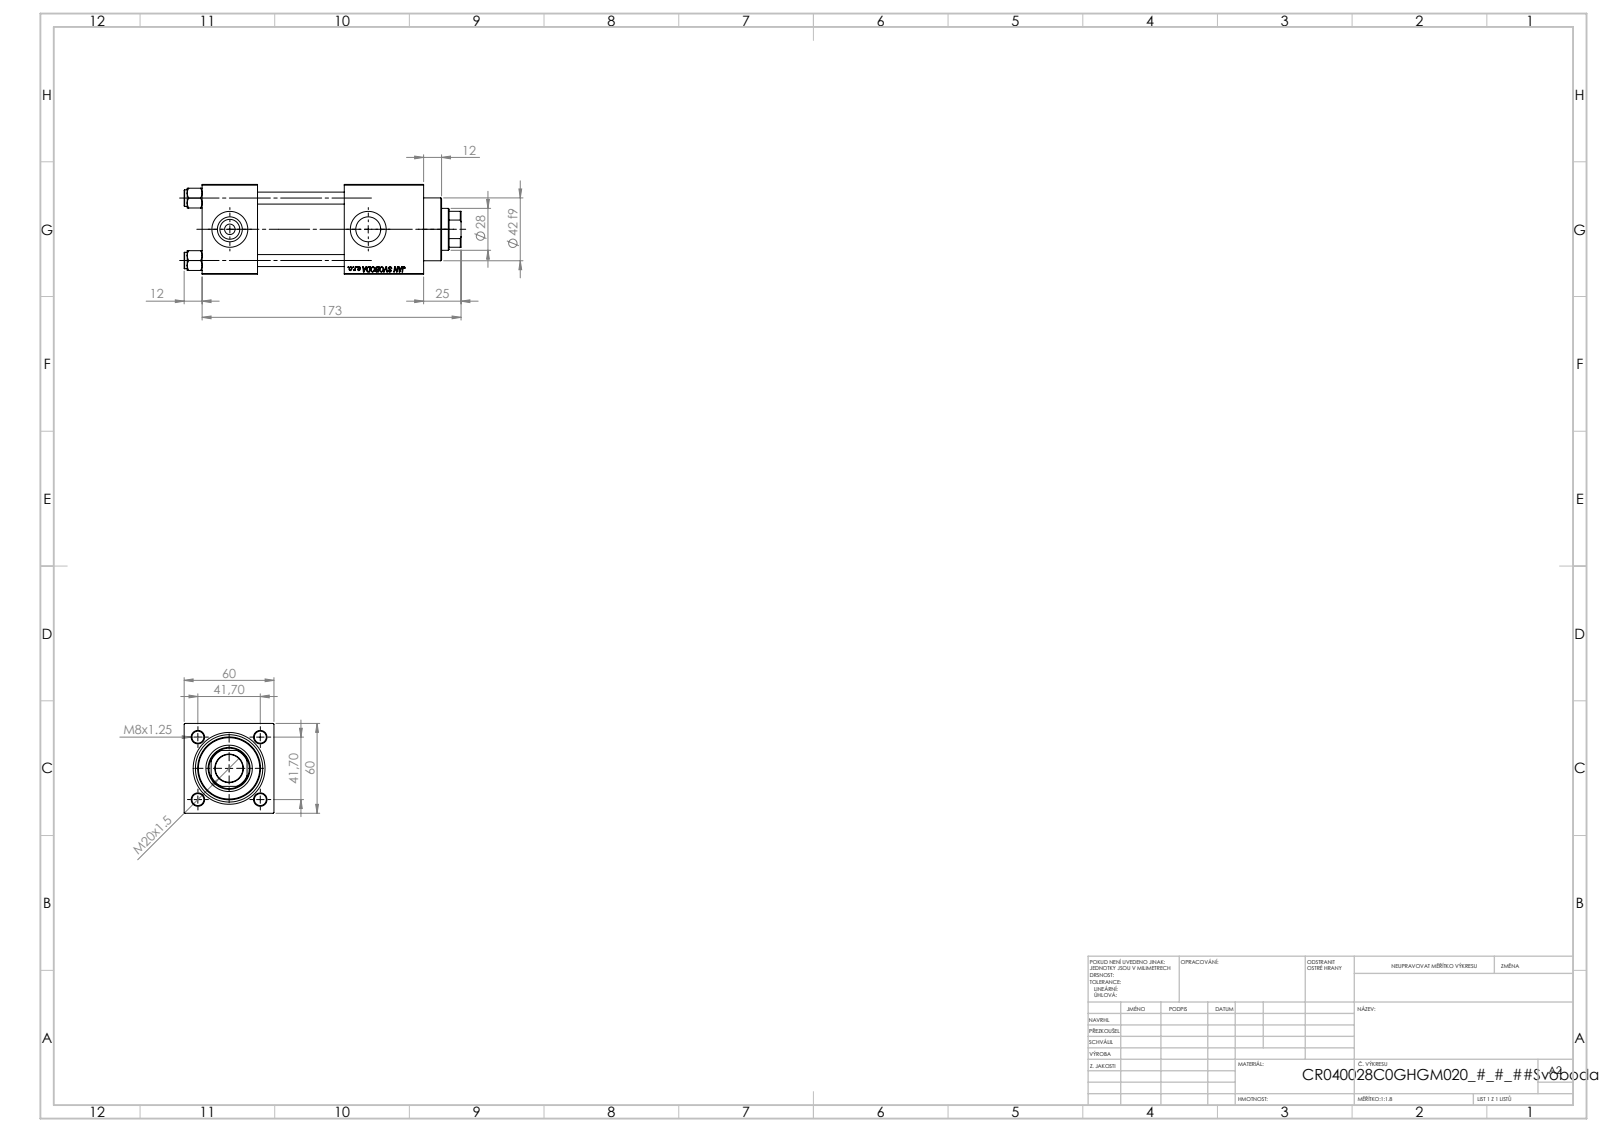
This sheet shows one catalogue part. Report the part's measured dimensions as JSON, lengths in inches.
{"part_name": "V215_VC_A; V215CR_VCP_C; V215CR_C_TYCINKA; NUT_M5_C (+1 more)", "step_written_by": "SolidWorks 2019 (CONFIG_CONTROL_DESIGN)", "units": "inches", "bodies": {"solids": 11, "faces": 1148, "planar": 526, "cylindrical": 86, "other": 536}, "overall_size": [7.283, 2.362, 2.362], "volume_in3": 25.89, "surface_area_in2": 172.7, "round_holes": [[0.315, 4], [0.276, 2], [0.656, 2], [0.945, 2], [0.728, 1], [1.102, 1], [1.22, 1], [1.575, 1], [1.772, 1]], "round_bosses_or_shafts": [[0.433, 4], [1.811, 1], [1.654, 1]], "partial_cylinders_radius": [[0.531, 1]], "face_to_face_distances": [2.362, 1.457, 2.283, 3.74, 2.087, 4.697, 3.24, 0.957, 5.827, 4.37], "hole_center_spacings": [1.161, 1.642, 2.322, 3.642]}
